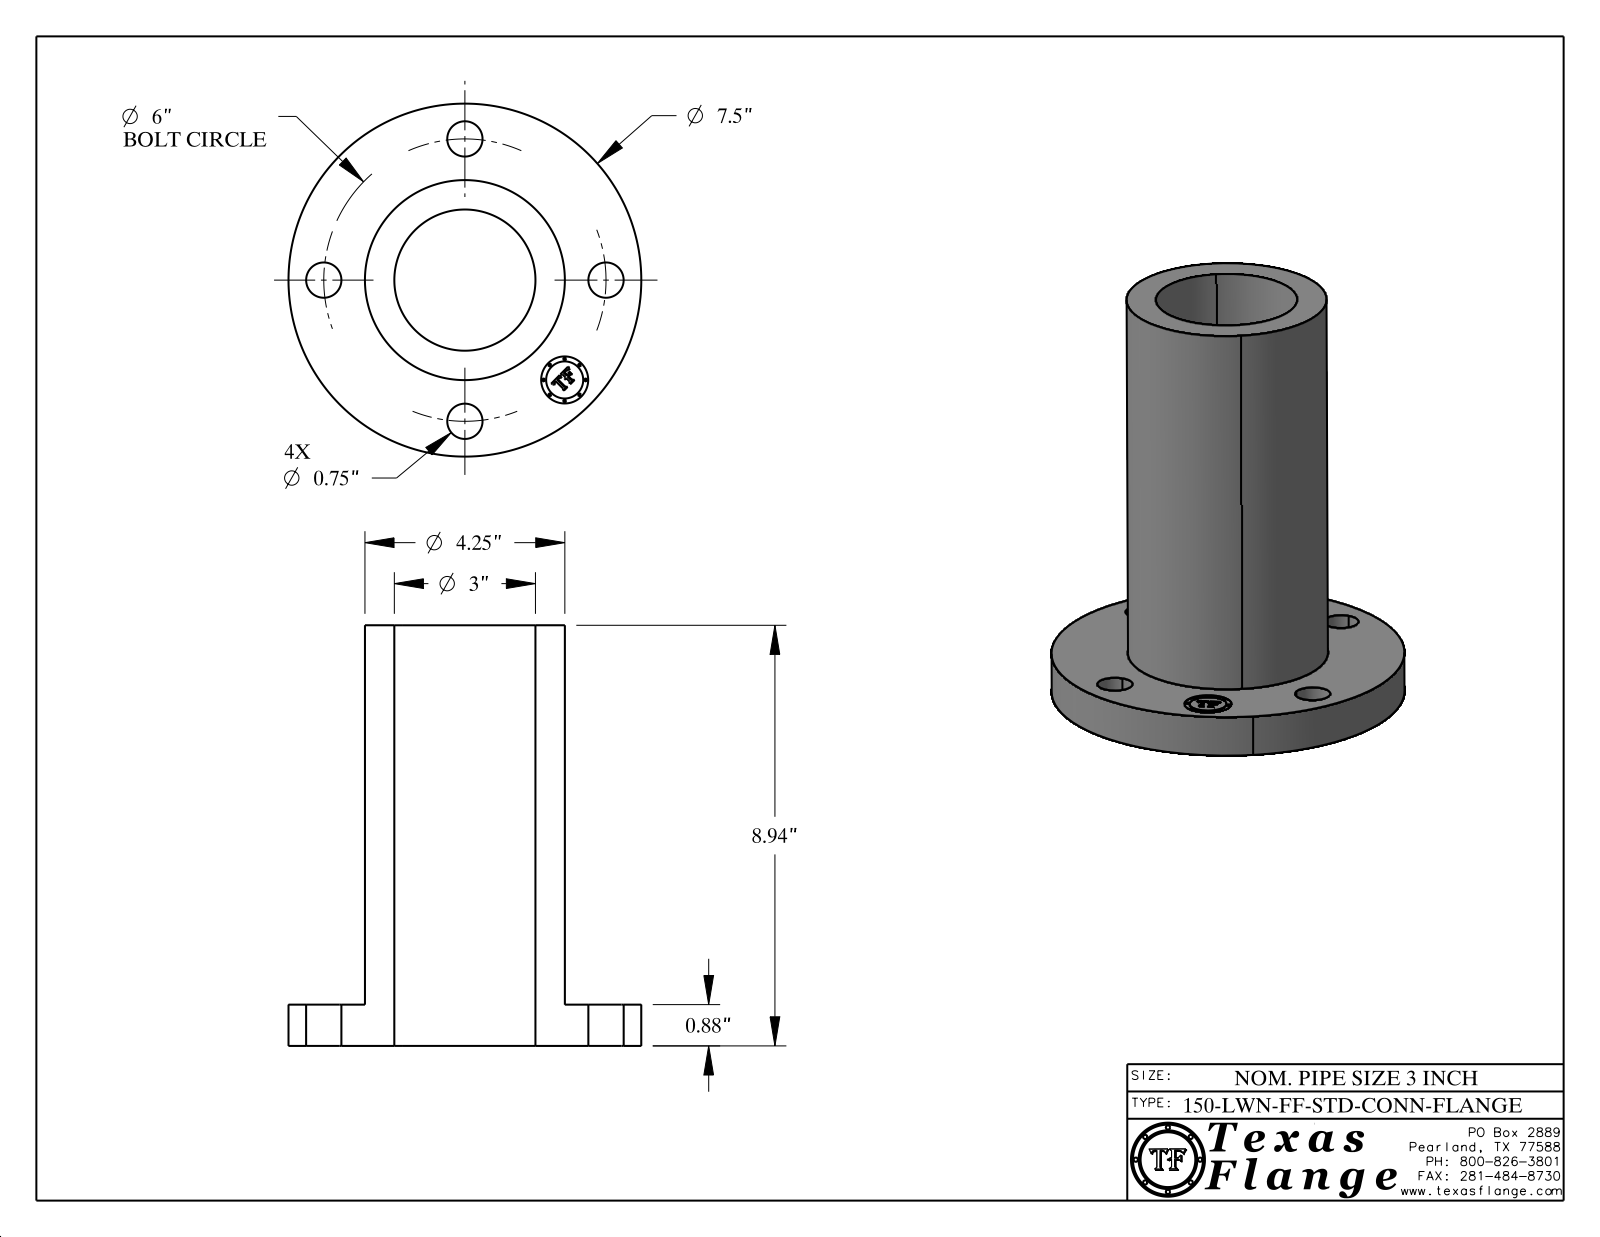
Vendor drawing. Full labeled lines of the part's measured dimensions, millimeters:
Part name (STEP PRODUCT): 3-150-LWN-FF-STD-CONN-FLANGE
STEP written by: CATIA V5 STEP AP214 (AUTOMOTIVE_DESIGN)
Units: millimetres
Bodies: 1 solid, 402 faces (368 planar, 34 cylindrical, 0 other)
Overall size (bounding box): 227 × 190.5 × 190.5
Volume: 1 448 000 mm³ · Surface area: 188 100 mm²
Round holes (diameter × count): ⌀19.1 ×4, ⌀25.4 ×1, ⌀76.2 ×1
Round bosses / shafts (diameter × count): ⌀1.5 ×8, ⌀190.5 ×1, ⌀108 ×1, ⌀20 ×1
Main face-to-face distances: 22.3, 227, 204.7, 22.1, 204.9, 7.6, 7.4, 1.4, 4.9, 6.3
Hole centre spacings: 76.2, 107.8, 58.3, 140.8, 152.4
